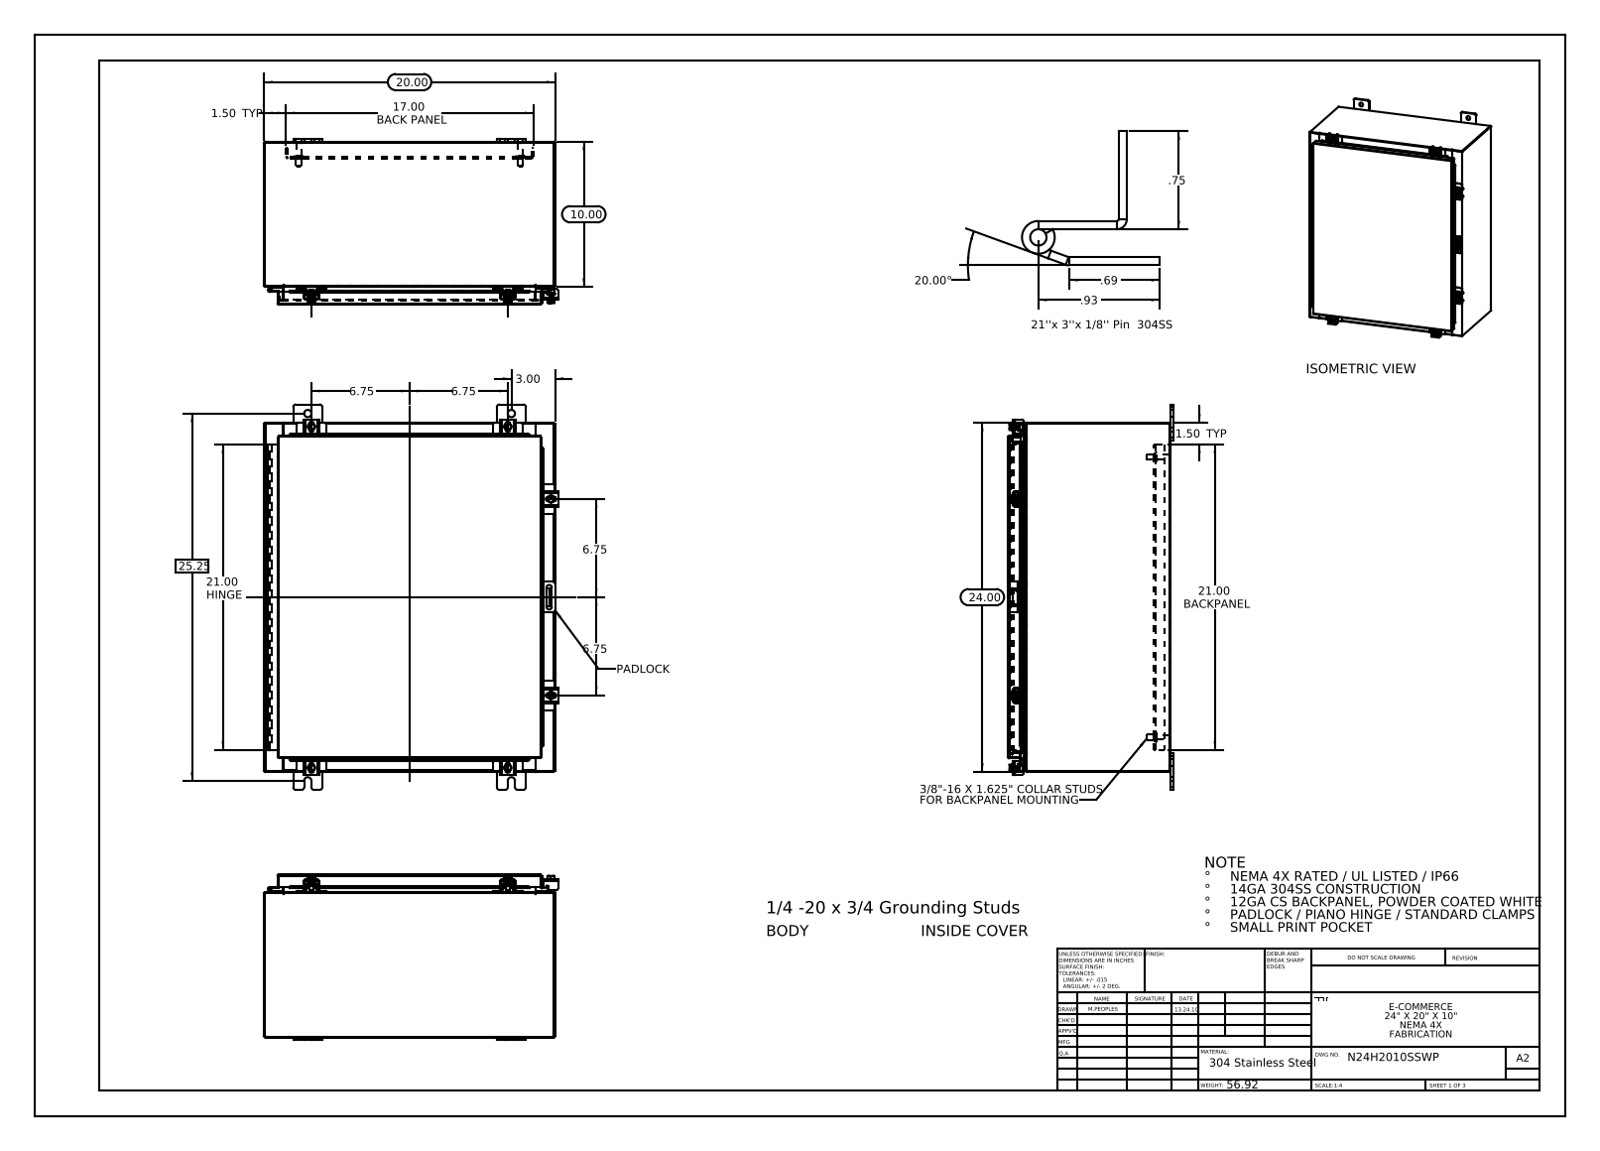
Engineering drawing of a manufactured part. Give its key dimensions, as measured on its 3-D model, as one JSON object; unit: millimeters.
{"part_name": "N24H2010SSWP Padlock Staple; N24H2010SSWP 125 Pin Hinge; N24H2010SSWP; N24H2010SSWP 22104005_DEFAULT (+8 more)", "step_written_by": "SolidWorks 2013 (CONFIG_CONTROL_DESIGN)", "units": "millimeters", "bodies": {"solids": 47, "faces": 1709, "planar": 908, "cylindrical": 705, "other": 96}, "overall_size": [673.1, 513.4, 289.3], "volume_mm3": 3277000, "surface_area_mm2": 3266000, "round_holes": [[12.7, 8], [5.4, 6], [6.6, 6], [3.2, 2], [3.2, 1]], "round_bosses_or_shafts": [[6.4, 7], [12.7, 6], [10.1, 6], [15.9, 4], [9.5, 4], [8.4, 4]], "partial_cylinders_radius": [[1.5, 30], [0.3, 25], [4.8, 24], [2.2, 21], [3, 12], [3.6, 12], [3.2, 10], [1.3, 9]], "face_to_face_distances": [1.9, 282.6, 506.1, 284.5, 280.7, 607.7, 2.6, 25.4, 27.3, 255.3], "hole_center_spacings": [542.8, 653.8, 342.9, 10.9, 23.7, 47.2, 57.8, 57.8]}
